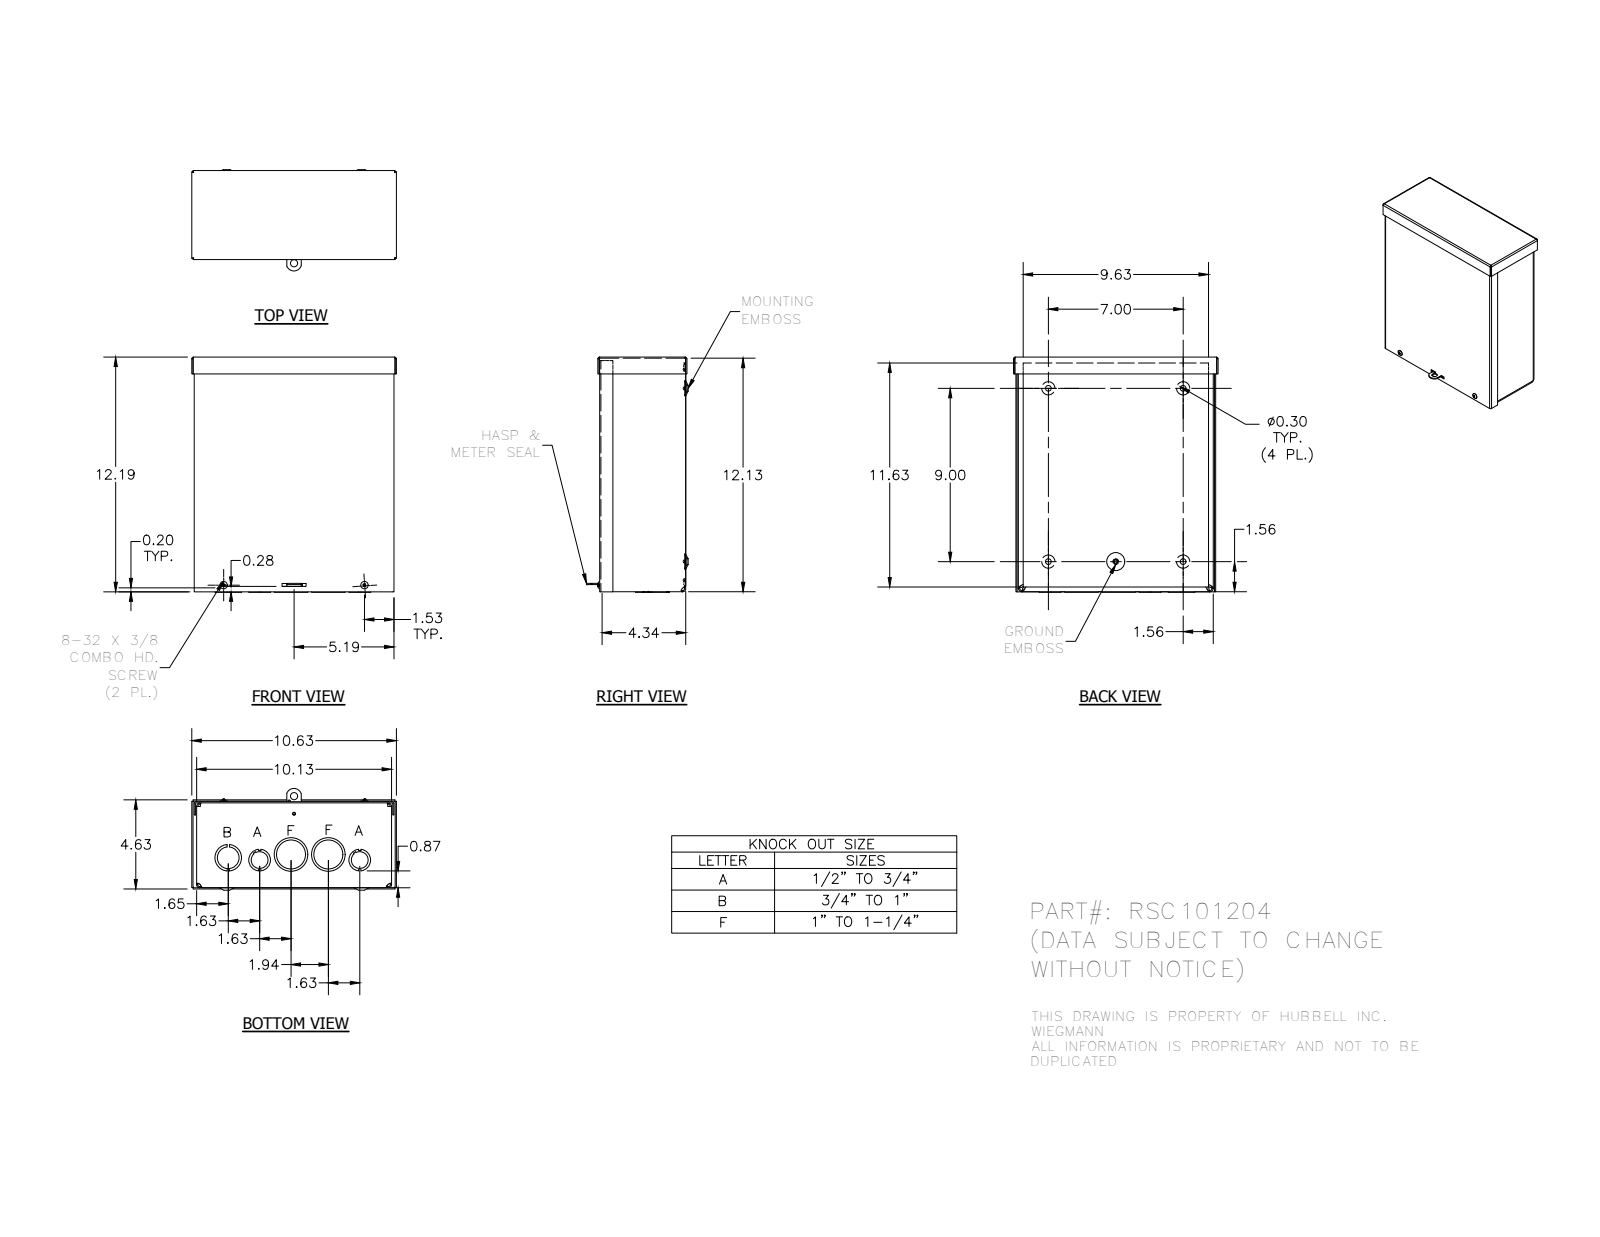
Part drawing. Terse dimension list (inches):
name: RSC101204; RSC101204_WRAP; RSC1012_LID; RSC1004_CAP (+4 more)
written by: Autodesk Inventor 2012 (AUTOMOTIVE_DESIGN)
unit: in
bodies: 7 solids, 518 faces (245 planar, 129 cylindrical, 144 other)
size: 12.281 × 10.625 × 5.125
volume: 35.43 in³; area: 1 160 in²
holes: 4× ⌀0.3, 4× ⌀0.313, 3× ⌀1.125, 2× ⌀0.125, 2× ⌀0.148, 2× ⌀0.875, 2× ⌀1.5, 2× ⌀1.75, 1× ⌀0.156, 1× ⌀0.165, 1× ⌀0.375, 1× ⌀1.375
bosses: 2× ⌀0.384, 2× ⌀0.164, 1× ⌀0.229
rounds: 10× R0.01, 8× R0.031, 8× R0.093, 8× R0.125, 8× R0.187, 4× R0.031, 4× R0.055, 4× R0.062
face distances: 0.062, 4.249, 4.187, 0.062, 0.063, 4.312, 4.25, 10.126, 0.124, 12.126
hole spacings: 1.072, 1.261, 1.656, 3.5, 3.582, 7, 7.313, 9
